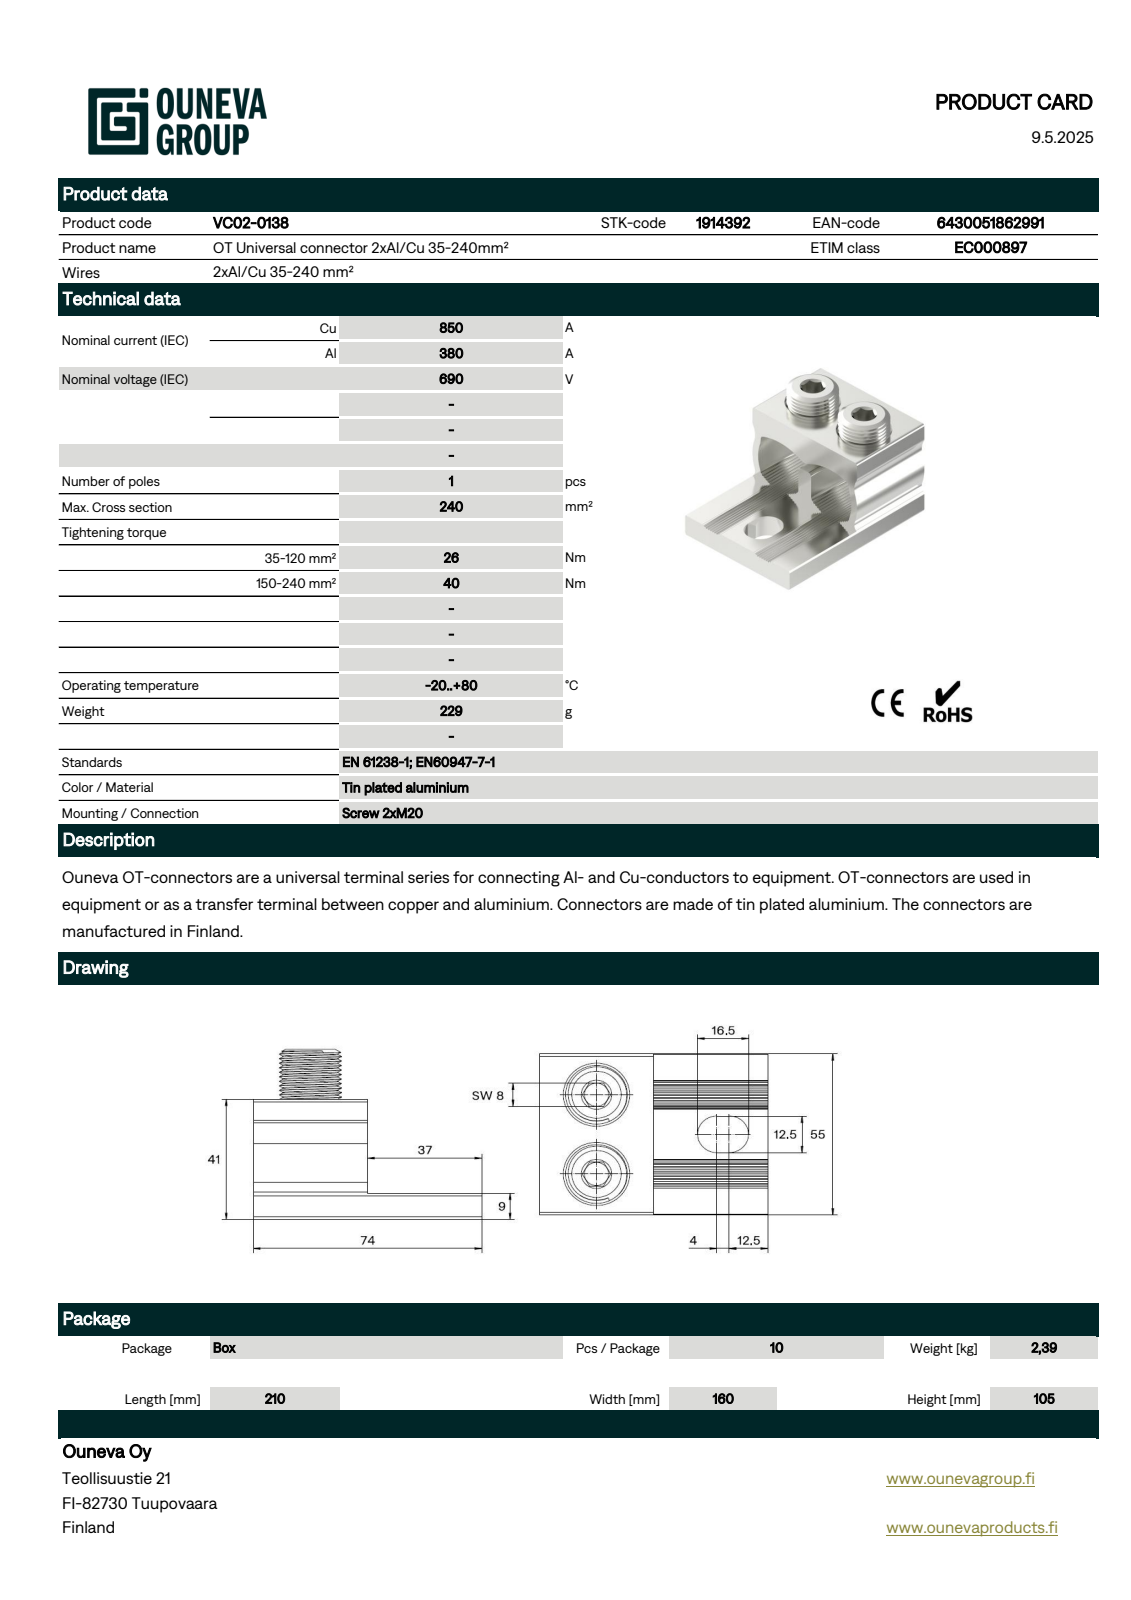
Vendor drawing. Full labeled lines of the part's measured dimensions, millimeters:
Part name (STEP PRODUCT): Liitinrunko OT 2x240
STEP written by: Creo Elements/Direct Modeling 20.6A 14-Oct-2023 (C) Parametric Technology GmbH (AUTOMOTIVE_DESIGN)
Units: millimetres
Bodies: 1 solid, 169 faces (46 planar, 111 cylindrical, 12 other)
Overall size (bounding box): 74 × 58 × 55
Volume: 74 809 mm³ · Surface area: 24 016 mm²
Round bosses / shafts (diameter × count): ⌀20 ×2
Partial cylindrical surfaces — rounded edges, fillets, slot ends (radius × count): R0.3 ×74, R2 ×6, R1 ×4, R1.5 ×4, R3 ×2, R3.5 ×2, R6.25 ×2, R6.5 ×2
Main face-to-face distances: 37, 41, 9, 32, 55, 24.14, 30.86, 74, 8, 6.72
